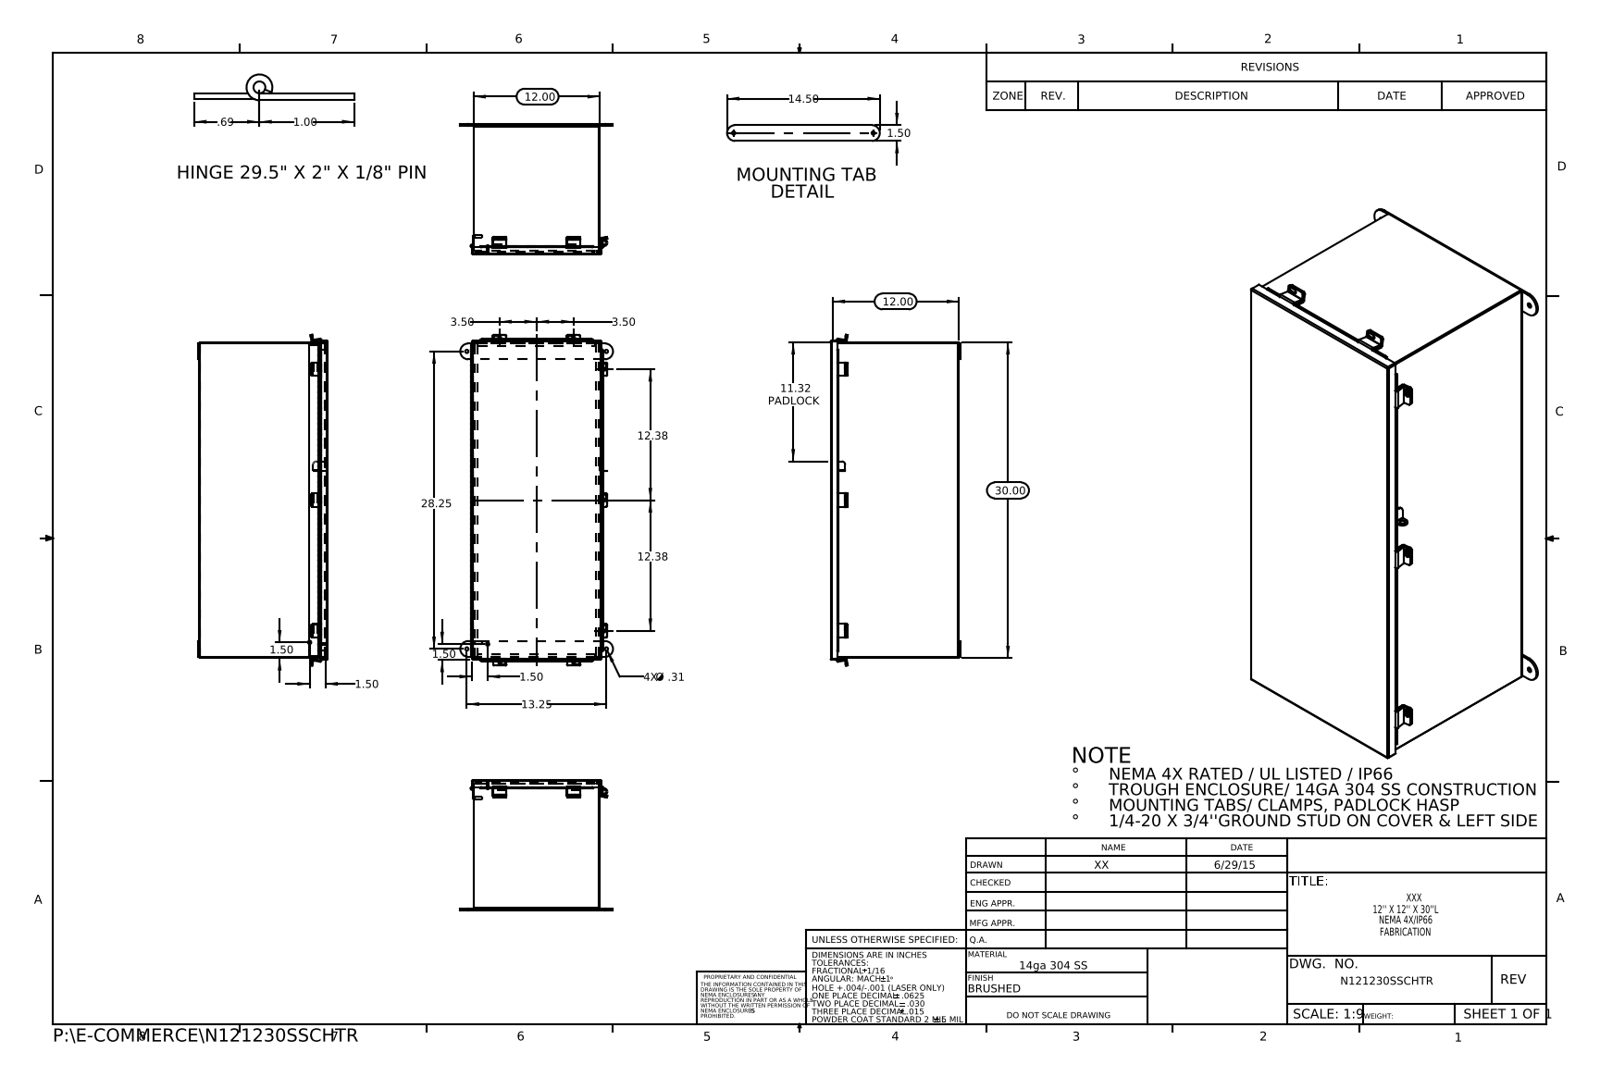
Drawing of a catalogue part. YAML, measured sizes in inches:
part_name: "N121230SSCHTR JIC Enclosure Template; N121230SSCHTR Hinge Body Side; N121230SSCHTR JIC Top; N121230SSCHTR _JIC Hinge (+8 more)"
step_written_by: "SolidWorks 2015 (CONFIG_CONTROL_DESIGN)"
units: inches
bodies: {solids: 25, faces: 1086, planar: 669, cylindrical: 397, other: 20}
overall_size: [31.407, 14.5, 12.337]
volume: 146.7
surface_area: 3915
round_holes:
  - {diameter: 0.25, count: 7}
  - {diameter: 0.313, count: 4}
  - {diameter: 0.125, count: 1}
  - {diameter: 0.125, count: 1}
  - {diameter: 0.375, count: 1}
round_bosses_or_shafts:
  - {diameter: 0.315, count: 2}
  - {diameter: 0.236, count: 2}
  - {diameter: 0.273, count: 1}
  - {diameter: 0.25, count: 1}
partial_cylinders:
  - {radius: 0.125, count: 26}
  - {radius: 0.133, count: 14}
  - {radius: 0.009, count: 12}
  - {radius: 0.013, count: 11}
  - {radius: 0.088, count: 11}
  - {radius: 0.083, count: 6}
  - {radius: 0.1, count: 6}
  - {radius: 0.75, count: 4}
face_to_face_distances: [0.075, 11.925, 12.128, 11.85, 12, 12.203, 12.053, 29.925, 29.85, 30]
hole_center_spacings: [7, 12.425, 13.25, 28.25, 31.203, 12.54, 24.85]
